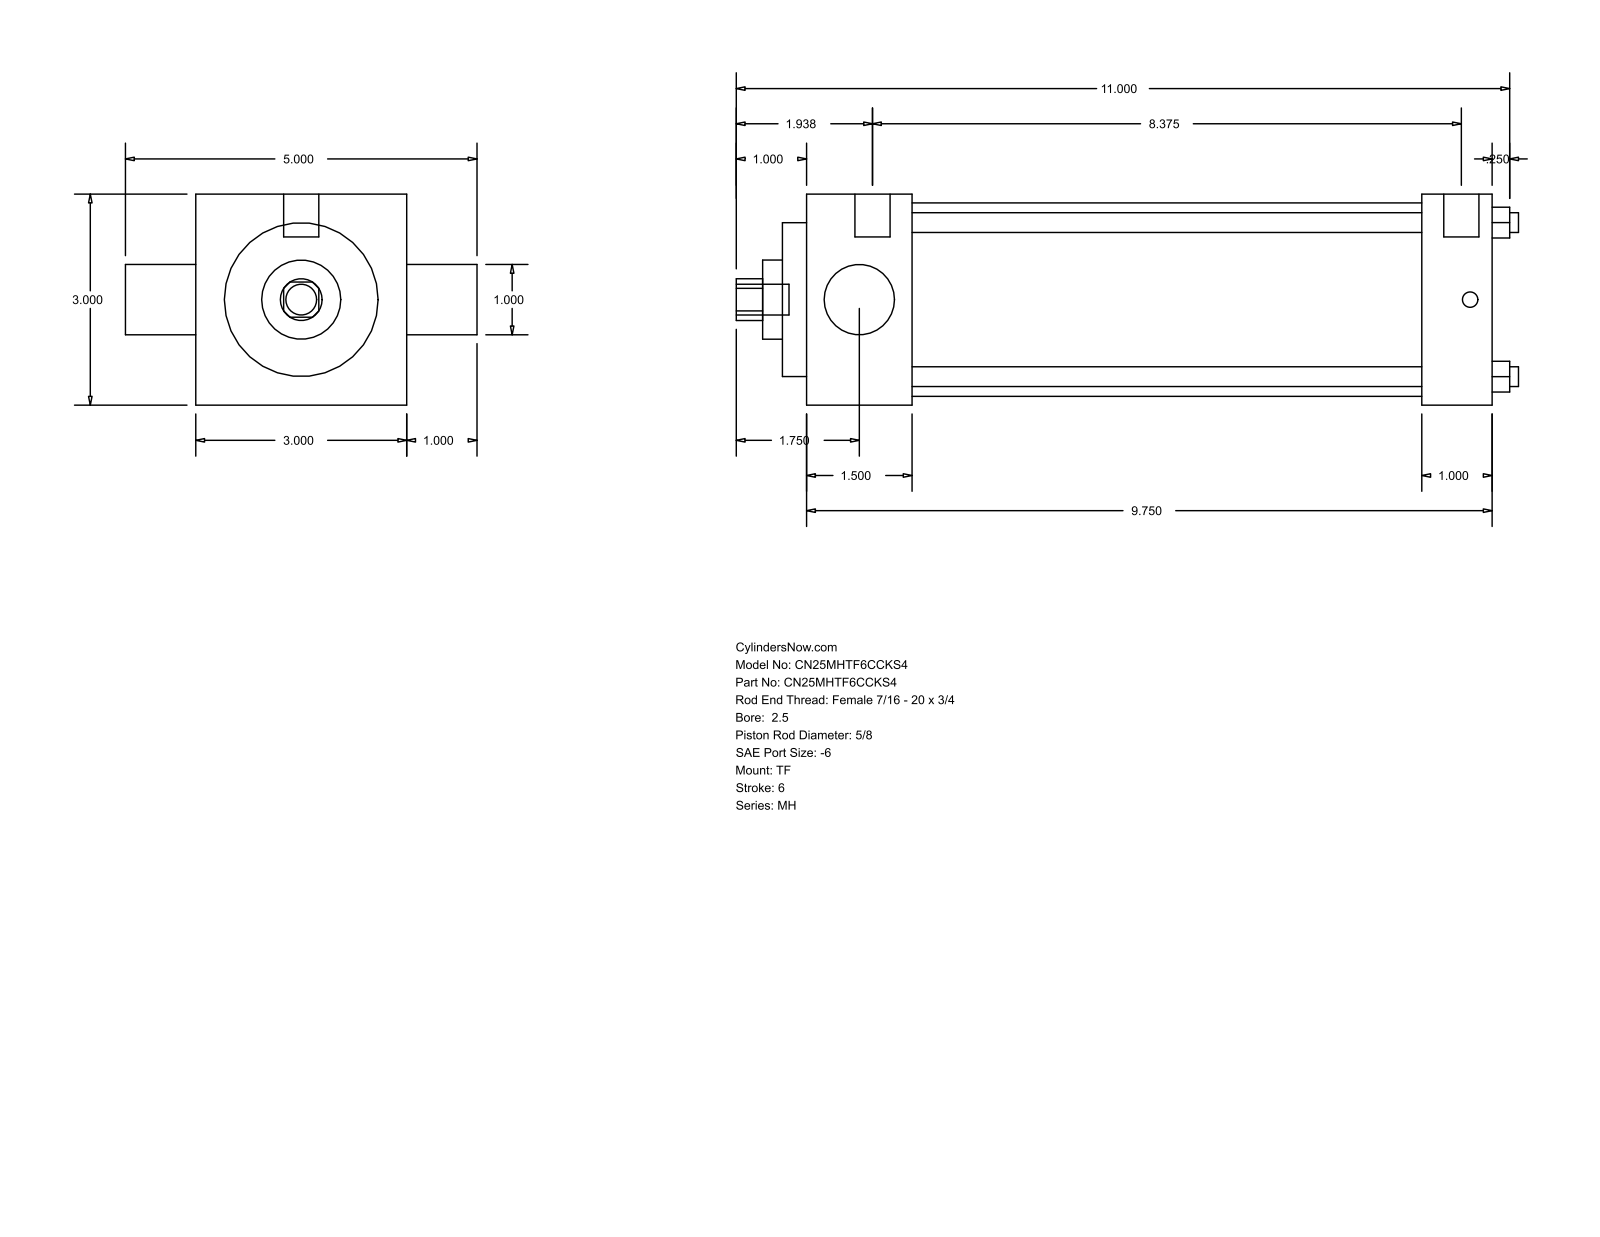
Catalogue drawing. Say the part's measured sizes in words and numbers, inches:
The part is named "MH_TF__0250_0.625". Its 3-D file was written by "GSSL Pune (CONFIG_CONTROL_DESIGN)". It is 0 solids with 86 faces: 61 planar, 25 cylindrical and 0 other. Overall it measures 11.125 by 5 by 3 inches. Round holes: 4 of diameter 0.281, 1 of diameter 0.625, 1 of diameter 1, 1 of diameter 1.125, 1 of diameter 2.187, 1 of diameter 2.75. Round bosses or shafts: 3 of diameter 0.219, 2 of diameter 0.5, 1 of diameter 0.437. Partial cylindrical surfaces (rounded edges, fillets, slot ends): 1 of radius 0.297. The main face-to-face distances are 3, 9.75, 1, 1.5, 8.25, 8.75, 7.25, 0.344, 1.844, 9.094. The hole center spacings are 1.548, 2.19, 3.097.
